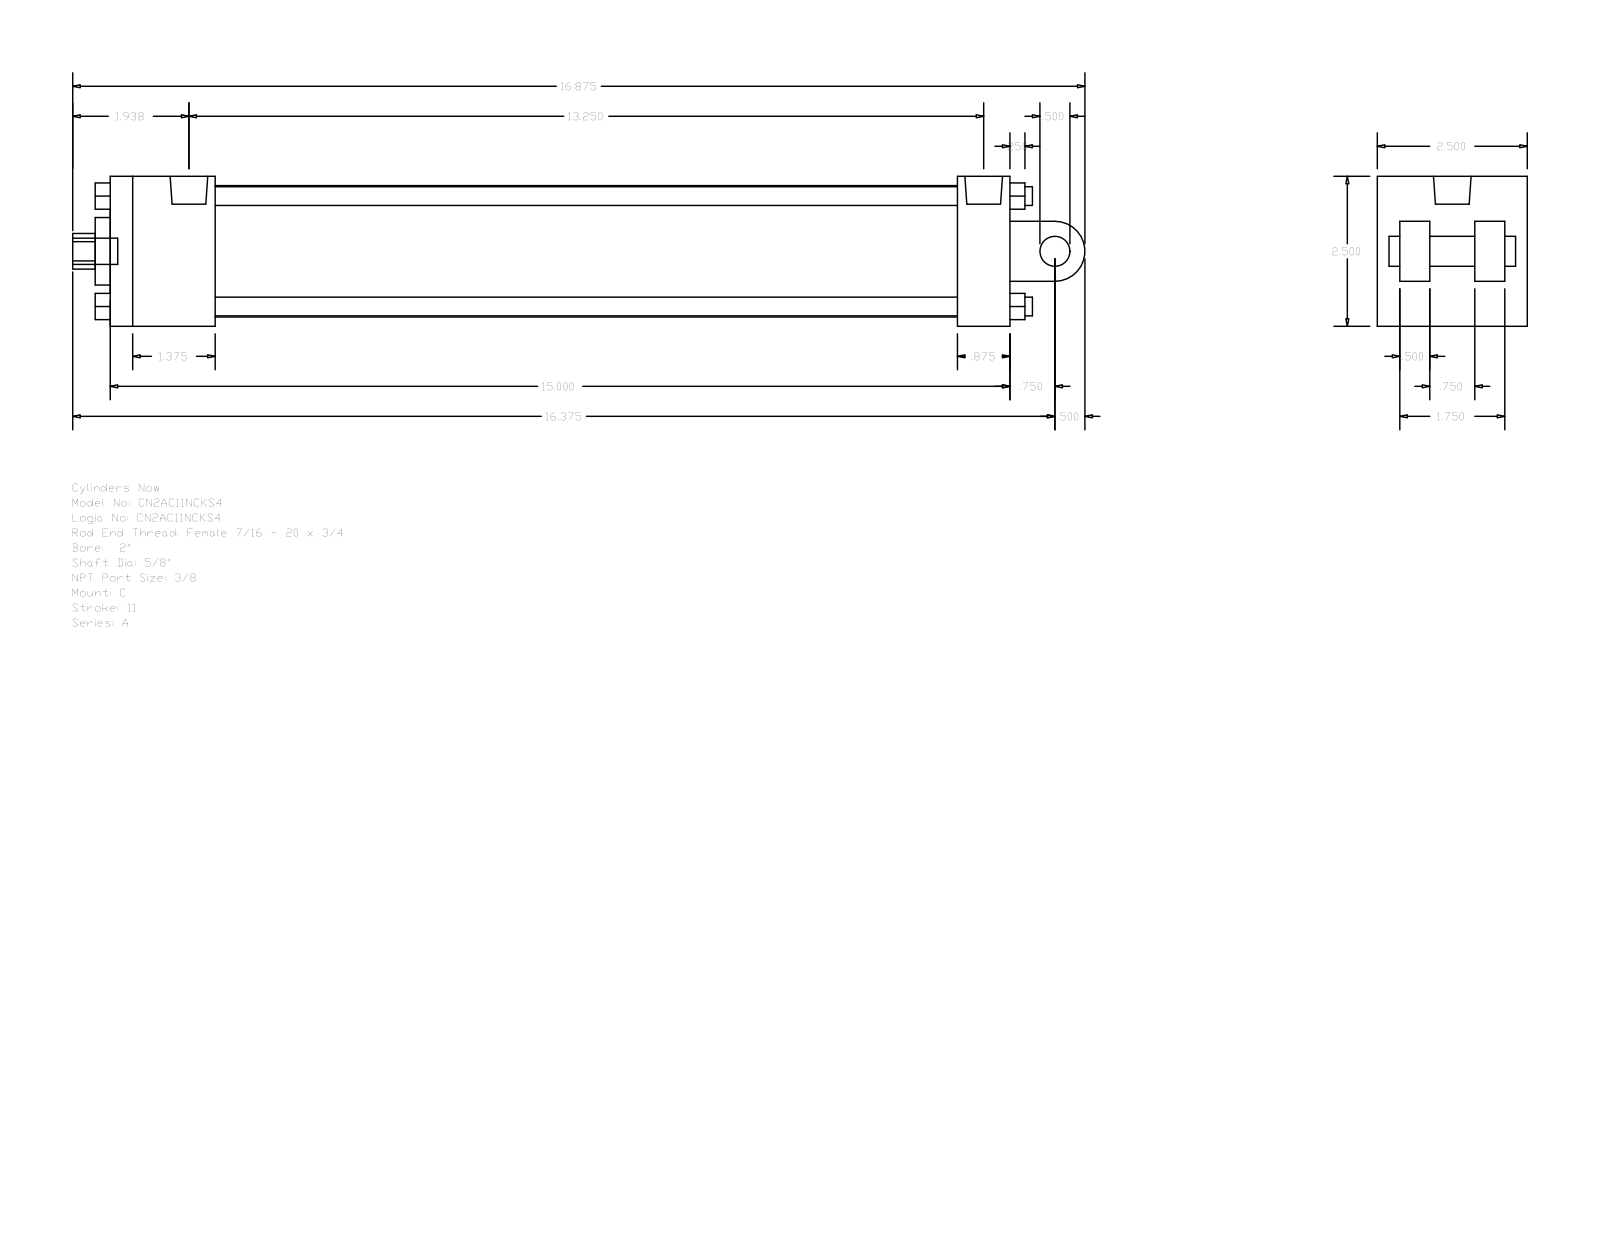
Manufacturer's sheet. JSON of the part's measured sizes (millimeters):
{"part_name": "A_C__0200_0.625", "step_written_by": "GSSL Pune (CONFIG_CONTROL_DESIGN)", "units": "millimeters", "bodies": {"solids": 0, "faces": 135, "planar": 102, "cylindrical": 33, "other": 0}, "overall_size": [428.62, 63.5, 63.5], "round_holes": [[5.56, 2], [15.88, 1], [15.93, 1], [28.57, 1], [55.63, 1]], "round_bosses_or_shafts": [[7.94, 4], [5.56, 2], [15.93, 1], [12.7, 1], [11.11, 1]], "partial_cylinders_radius": [[7.54, 1], [12.7, 1]], "face_to_face_distances": [63.5, 381, 44.45, 9.52, 336.55, 358.77, 314.32, 22.23, 12.7, 41.28], "hole_center_spacings": [3.97]}
